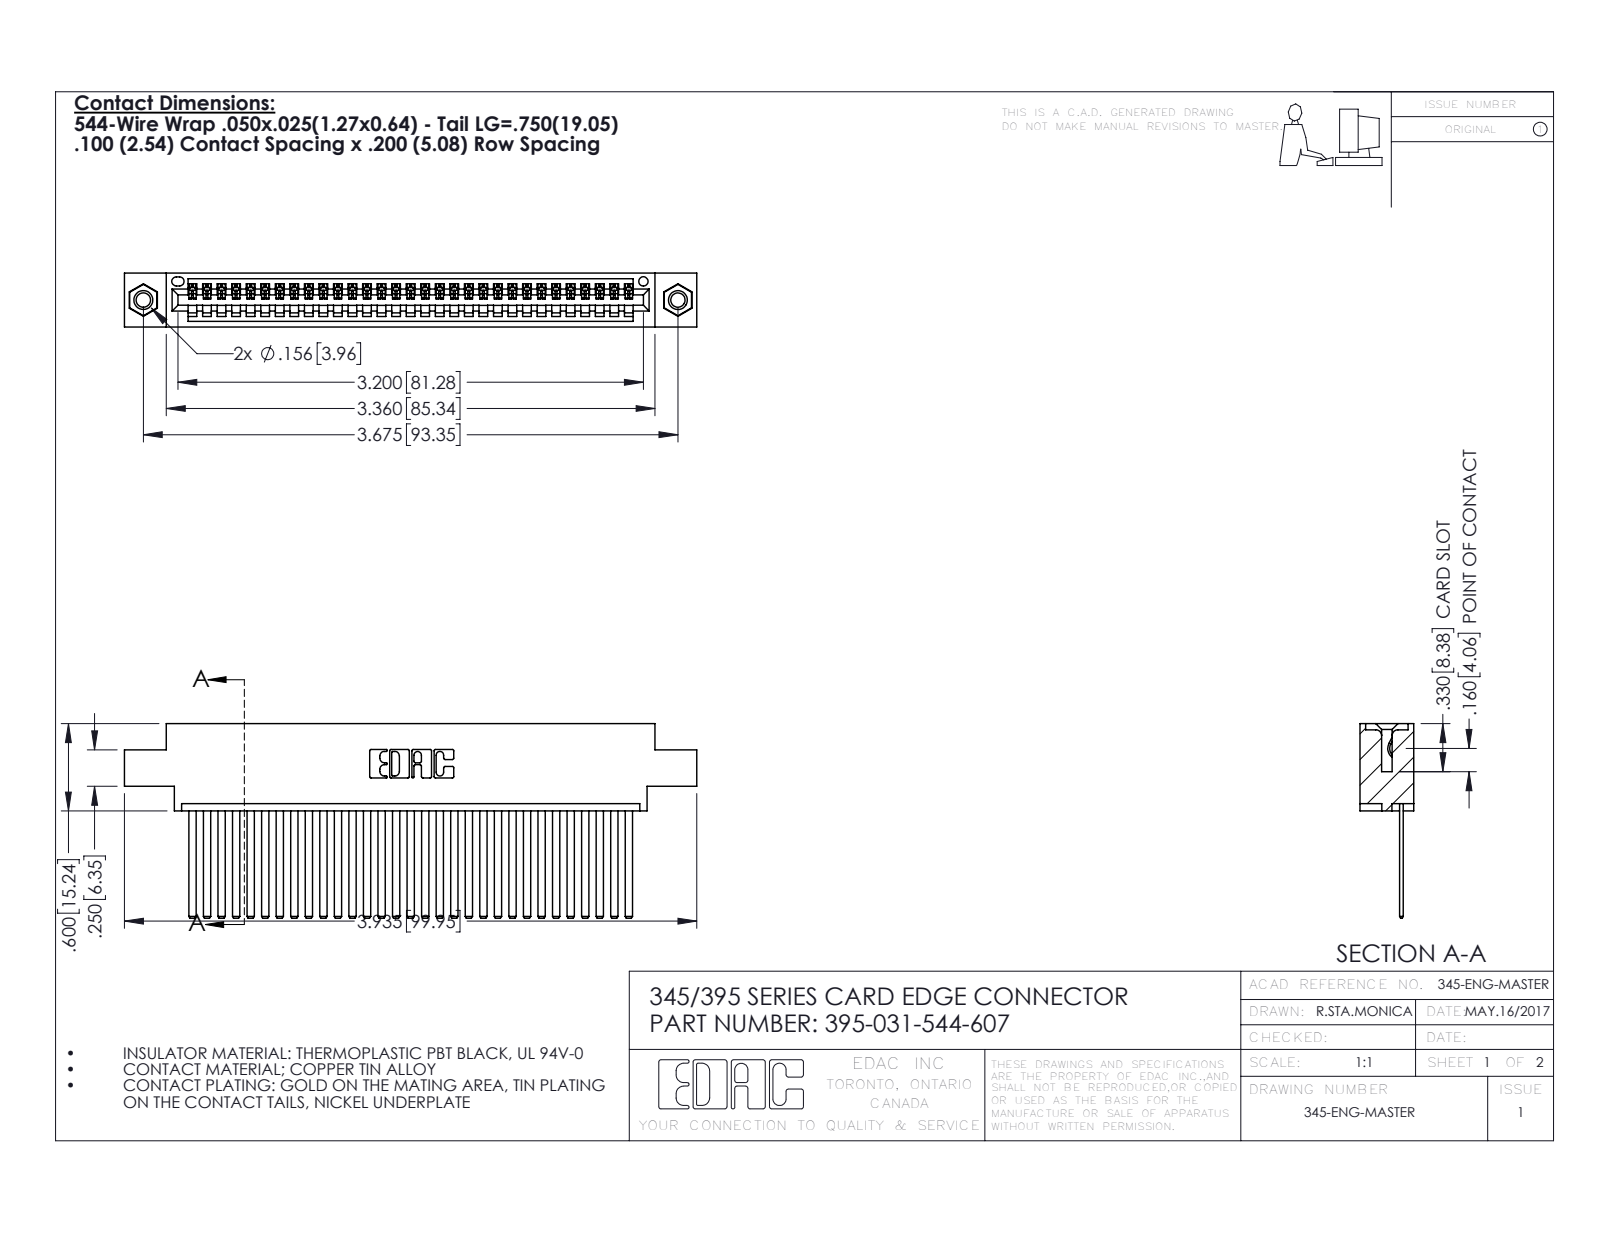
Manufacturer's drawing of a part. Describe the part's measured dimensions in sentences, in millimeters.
The part is named "345-250-001_345-250-005-103; 395-031-544-607; 345-292-001_345-293-144; 345 Part_0.170 Offset - 0.156 Dia-TI". Its 3-D file was written by "SolidWorks 2016 (CONFIG_CONTROL_DESIGN)". It is 34 solids with 1802 faces: 1232 planar, 554 cylindrical and 16 other. Overall it measures 99.9 by 34 by 9.4 millimeters. Its volume is 9 640 cubic millimeters and its surface area 13 890 square millimeters. Round holes: 2 of diameter 2.5, 2 of diameter 3.2, 2 of diameter 4, 1 of diameter 1.6. Round bosses or shafts: 2 of diameter 3.9. Partial cylindrical surfaces (rounded edges, fillets, slot ends): 62 of radius 0.2, 22 of radius 0.3, 6 of radius 0.2, 6 of radius 0.8, 3 of radius 0.7, 2 of radius 0.8, 2 of radius 1, 1 of radius 0.4. The main face-to-face distances are 1.8, 7.6, 0.6, 2.5, 6.9, 9.4, 5.1, 5.7, 4.4, 3.8. The hole center spacings are 6.9, 87.4, 93.3.
